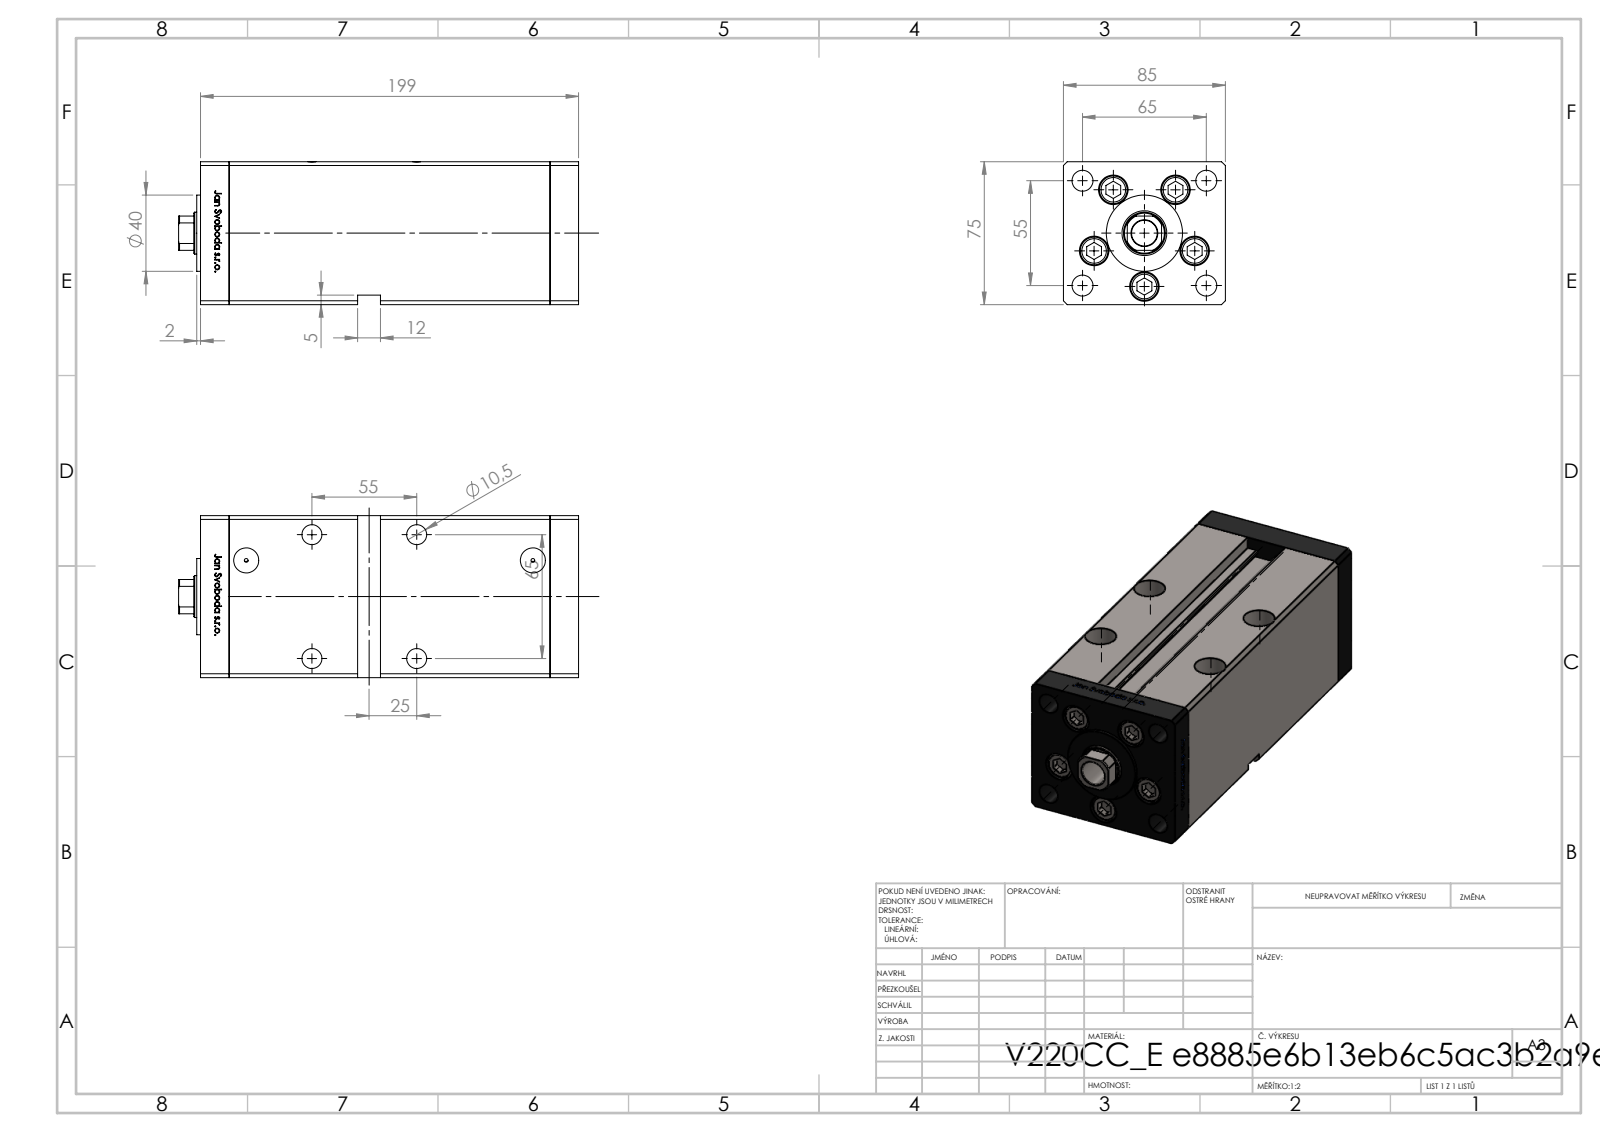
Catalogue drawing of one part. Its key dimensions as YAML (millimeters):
part_name: "V220C BACK_E; V220C_E MIDDLE; V220C_FRONT_E; V220C_VC_E (+1 more)"
step_written_by: "SolidWorks 2019 (CONFIG_CONTROL_DESIGN)"
units: millimeters
bodies: {solids: 14, faces: 1214, planar: 475, cylindrical: 165, other: 574}
overall_size: [210, 85, 75]
volume: 1076000
surface_area: 182851
round_holes:
  - {diameter: 11, count: 9}
  - {diameter: 15.5, count: 5}
  - {diameter: 10.5, count: 4}
  - {diameter: 16.5, count: 4}
  - {diameter: 2, count: 2}
  - {diameter: 13.16, count: 2}
  - {diameter: 13.5, count: 1}
  - {diameter: 22, count: 1}
  - {diameter: 23.5, count: 1}
round_bosses_or_shafts:
  - {diameter: 14.5, count: 5}
  - {diameter: 8, count: 5}
  - {diameter: 40, count: 1}
partial_cylinders:
  - {radius: 0.93, count: 2}
  - {radius: 10.5, count: 1}
face_to_face_distances: [85, 75, 15, 168.5, 183.5, 198.5, 34.25, 10.5, 64.5, 68.5]
hole_center_spacings: [28, 42.57, 55, 65, 85.15, 16.86, 19.17, 32.33]
